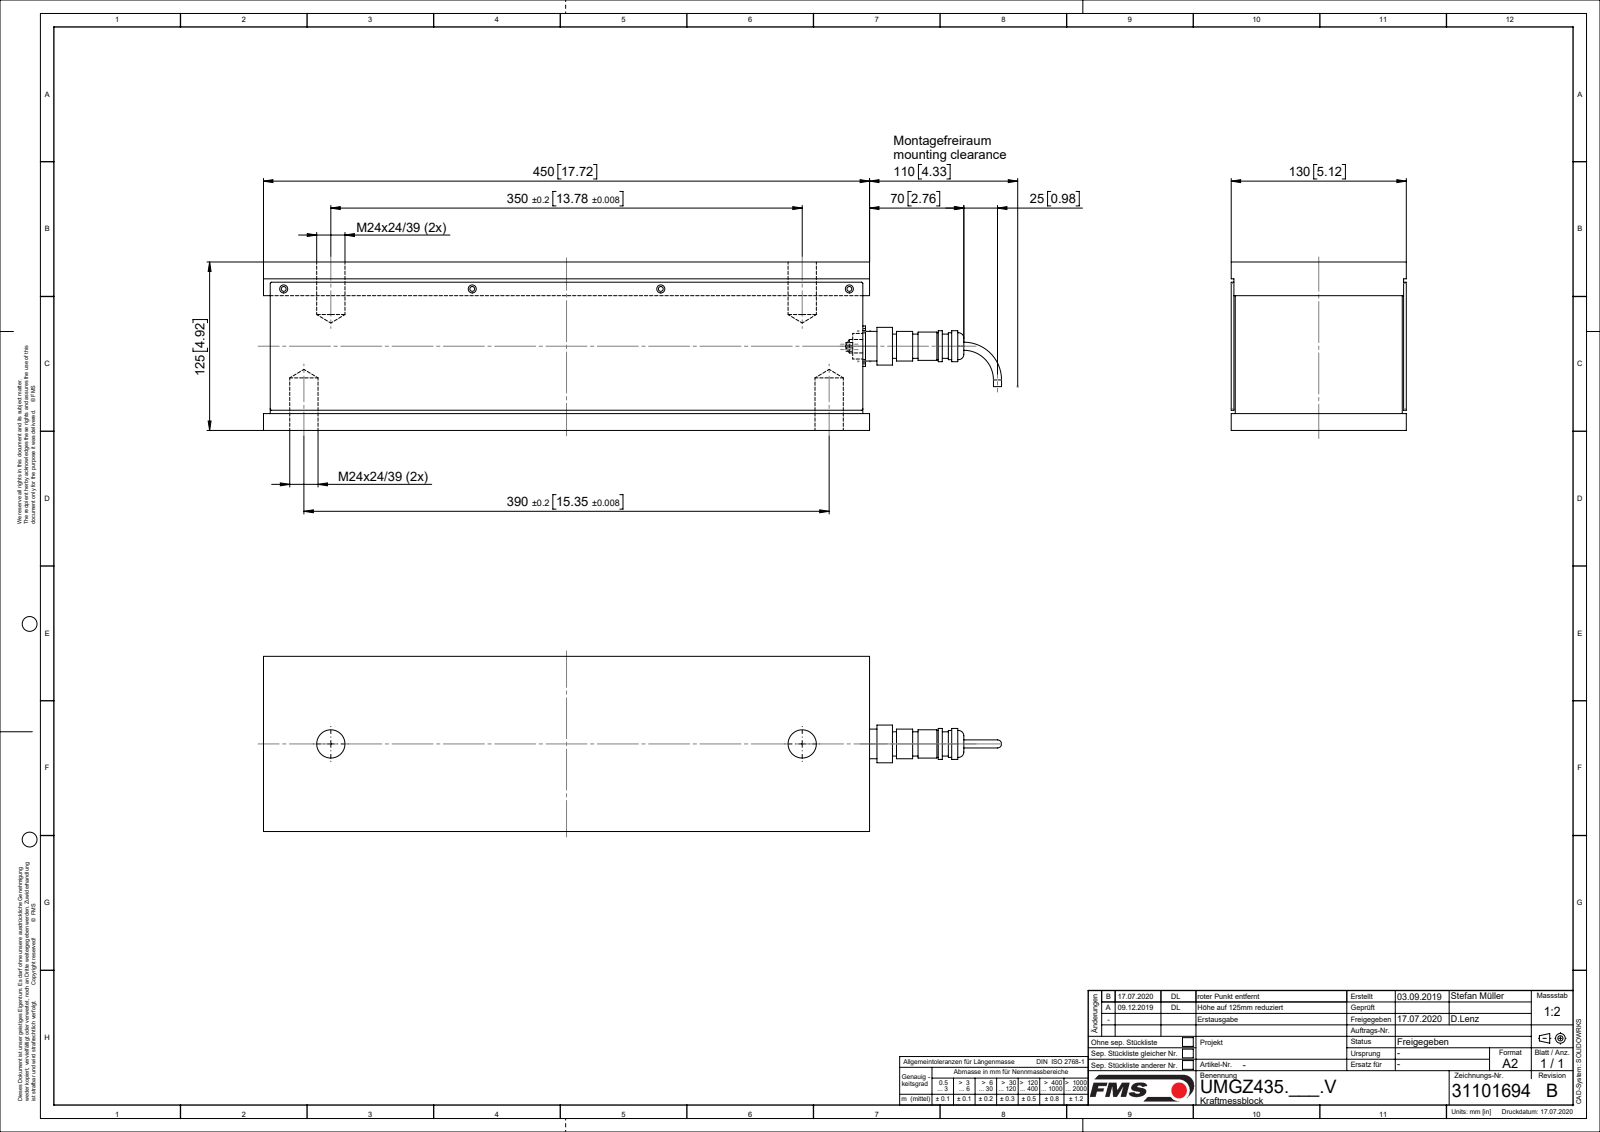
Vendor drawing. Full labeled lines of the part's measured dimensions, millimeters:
Part name (STEP PRODUCT): 31101694_A; 51585_01; 31101648_01; 31102358_01
STEP written by: SolidWorks 2018 (CONFIG_CONTROL_DESIGN)
Units: millimetres
Bodies: 4 solids, 186 faces (56 planar, 100 cylindrical, 30 other)
Overall size (bounding box): 548 × 130 × 125
Volume: 7 088 000 mm³ · Surface area: 459 109 mm²
Round holes (diameter × count): ⌀3.2 ×4, ⌀3.6 ×4, ⌀6 ×4, ⌀21 ×4, ⌀10 ×1
Round bosses / shafts (diameter × count): ⌀2.5 ×4, ⌀28 ×1, ⌀23 ×1, ⌀22 ×1, ⌀21 ×1, ⌀20 ×1, ⌀19 ×1, ⌀18 ×1
Partial cylindrical surfaces — rounded edges, fillets, slot ends (radius × count): R1 ×4, R4 ×4
Main face-to-face distances: 125, 2, 128, 3, 1, 127, 130, 126, 124, 440
Hole centre spacings: 16.26, 23, 140, 20, 32.53, 280, 370, 350
